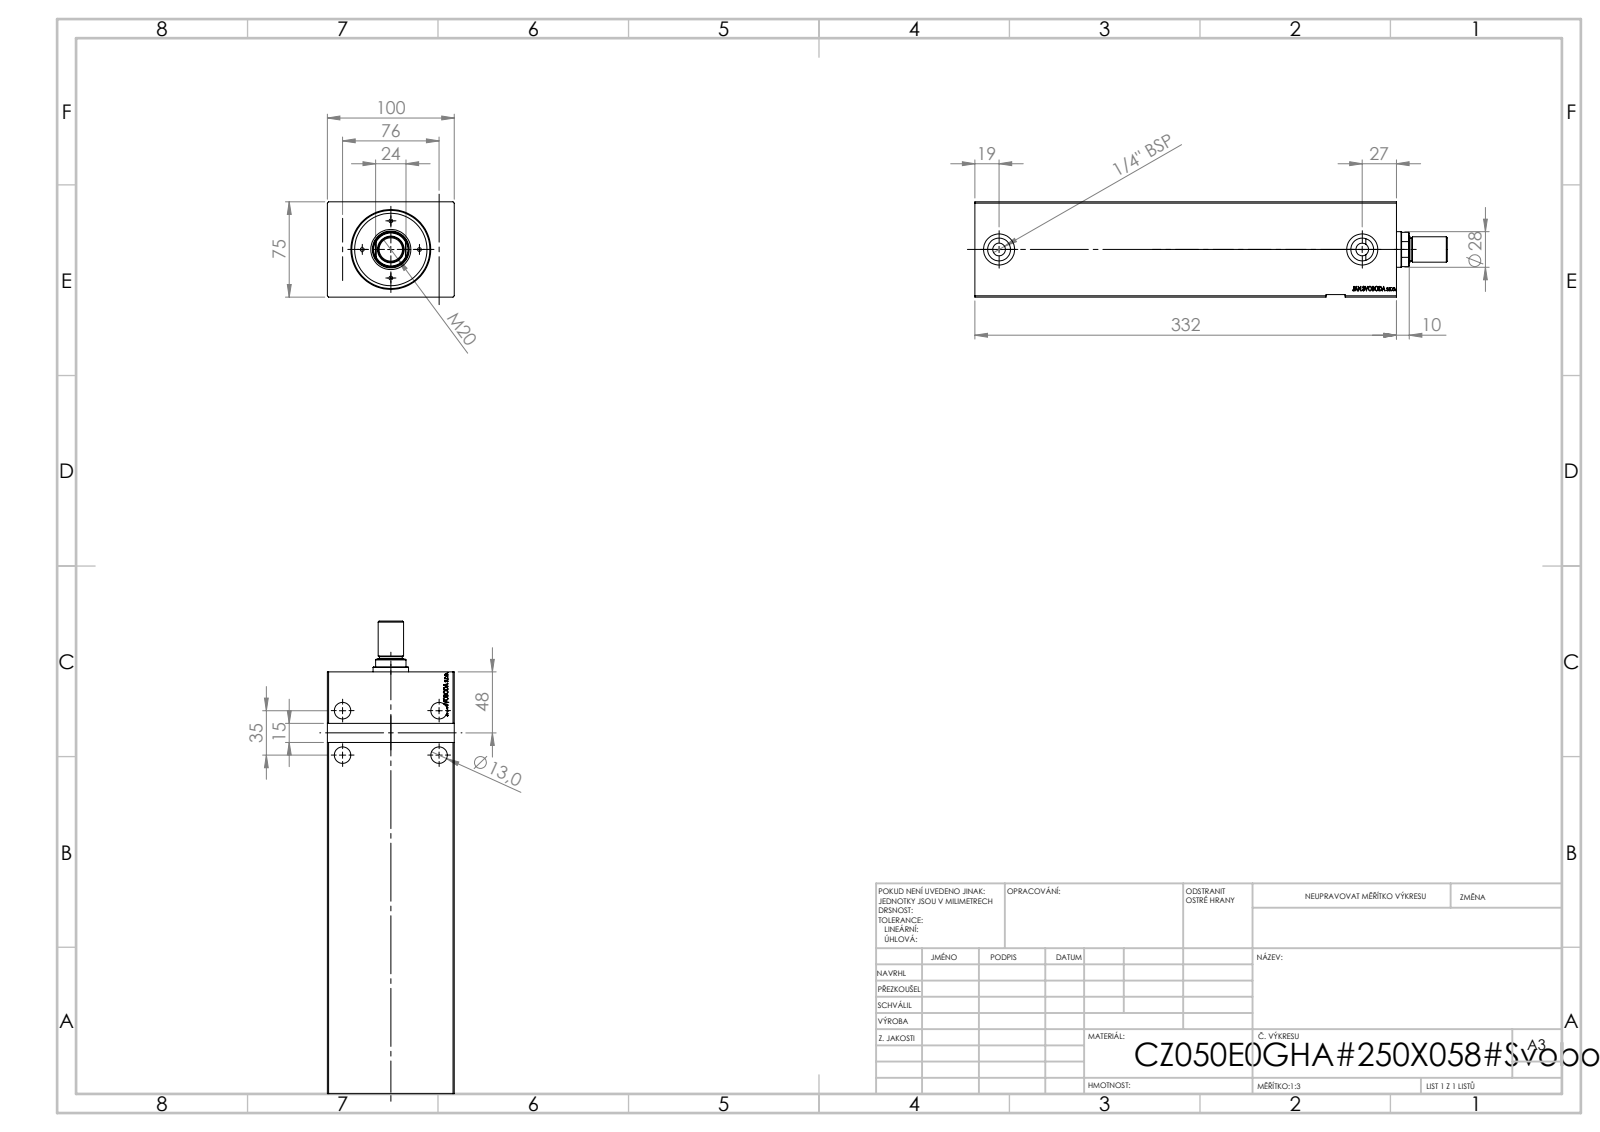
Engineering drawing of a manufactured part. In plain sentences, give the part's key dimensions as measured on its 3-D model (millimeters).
Its 3-D file was written by "SolidWorks 2019 (CONFIG_CONTROL_DESIGN)". It is 1 solid with 776 faces: 375 planar, 31 cylindrical and 370 other. Overall it measures 332 by 100 by 75 millimeters. Its volume is 1 812 000 cubic millimeters and its surface area 193 022 square millimeters. Round holes: 4 of diameter 13, 2 of diameter 8, 2 of diameter 10, 2 of diameter 18, 2 of diameter 24.5, 1 of diameter 36, 1 of diameter 50, 1 of diameter 61.5. The main face-to-face distances are 75, 100, 332, 314.2, 17.8, 2, 73, 331.8, 17.6, 10. The hole center spacings are 35, 76, 83.67, 21.03, 34.82, 56.38, 62.84, 238.34.
